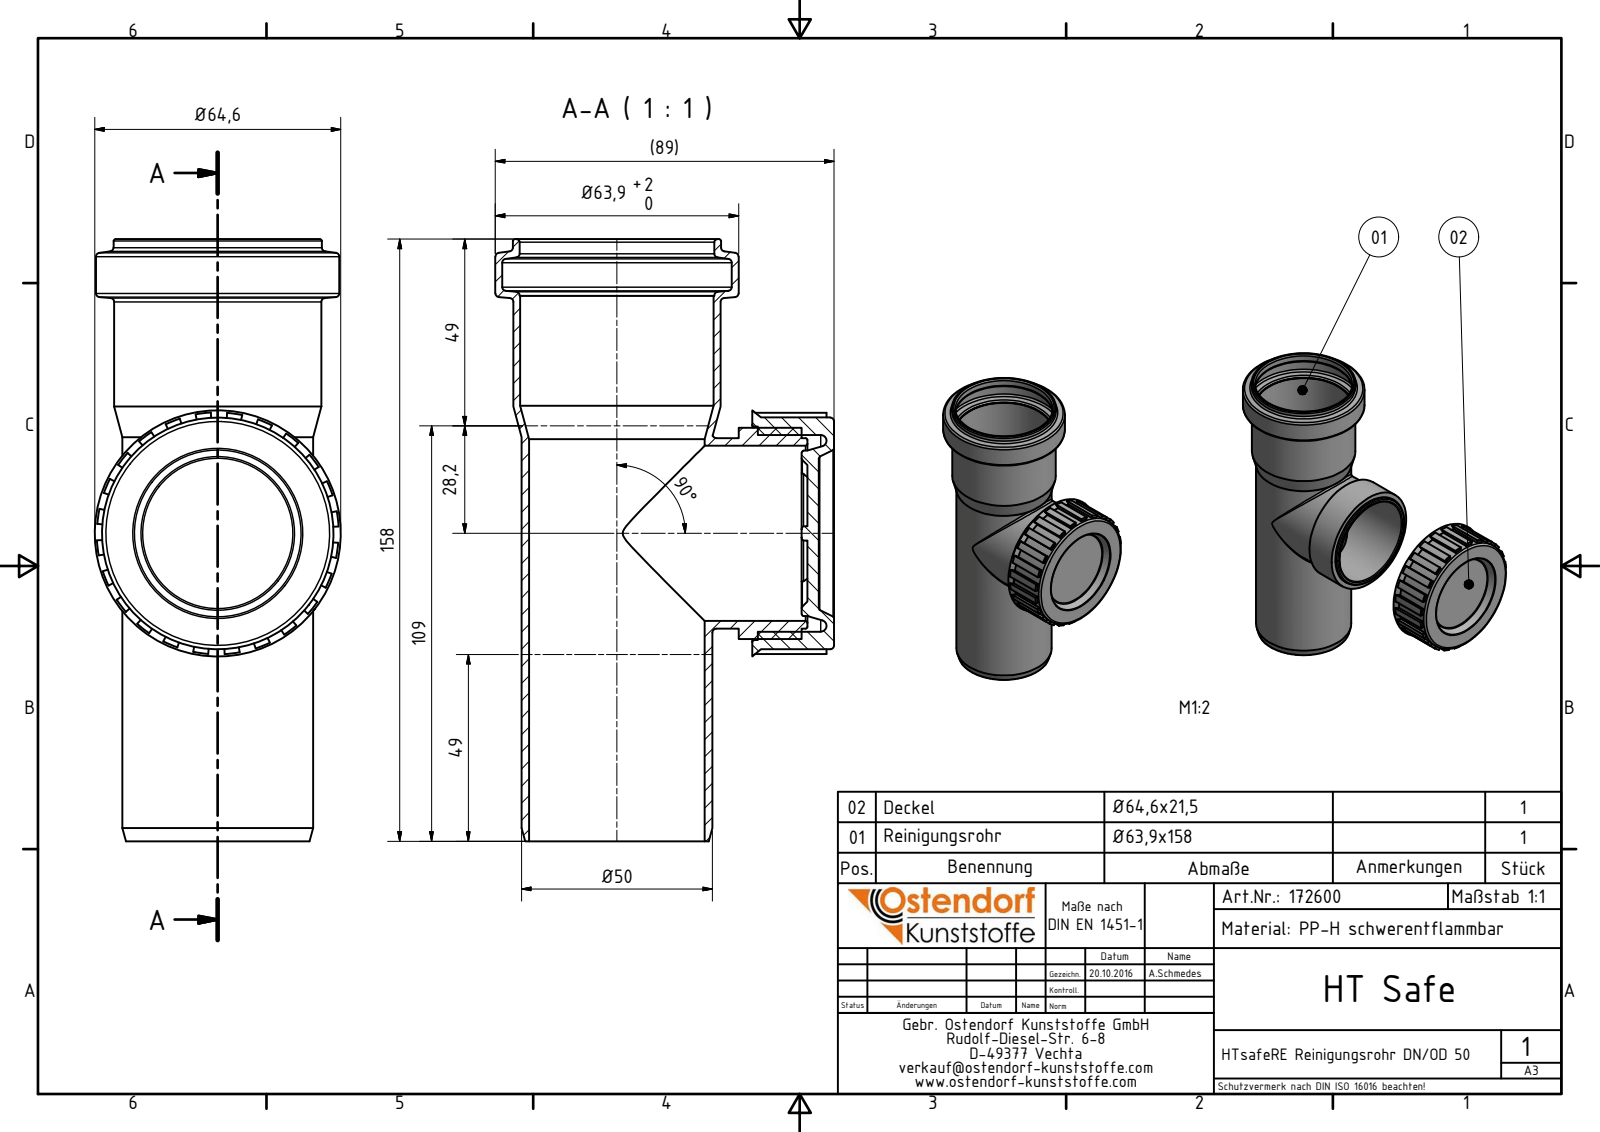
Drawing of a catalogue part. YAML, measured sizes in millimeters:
part_name: "112600 HTRE DN_OD 50; 112600 HTRE DN_OD 50 Deckel; 172600 HTsafeRE DN_OD 50 Zusammenbau"
step_written_by: "Autodesk Inventor 2016 (AUTOMOTIVE_DESIGN)"
units: millimeters
bodies: {solids: 2, faces: 181, planar: 95, cylindrical: 49, other: 37}
overall_size: [158, 88.95, 64.6]
volume: 90466
surface_area: 75878
round_holes:
  - {diameter: 46, count: 1}
  - {diameter: 46.1, count: 1}
  - {diameter: 50.8, count: 1}
  - {diameter: 51.1, count: 1}
  - {diameter: 51.6, count: 1}
  - {diameter: 56, count: 1}
  - {diameter: 60.3, count: 1}
round_bosses_or_shafts:
  - {diameter: 63.9, count: 1}
  - {diameter: 60.8, count: 1}
  - {diameter: 55.42, count: 1}
  - {diameter: 54.7, count: 1}
  - {diameter: 54.4, count: 1}
  - {diameter: 50.1, count: 1}
  - {diameter: 50, count: 1}
  - {diameter: 43.4, count: 1}
partial_cylinders:
  - {radius: 0.5, count: 4}
  - {radius: 31.75, count: 1}
face_to_face_distances: [4, 1.5, 13, 7, 3, 8.5, 4.5, 21.5, 17.5, 14.5]
